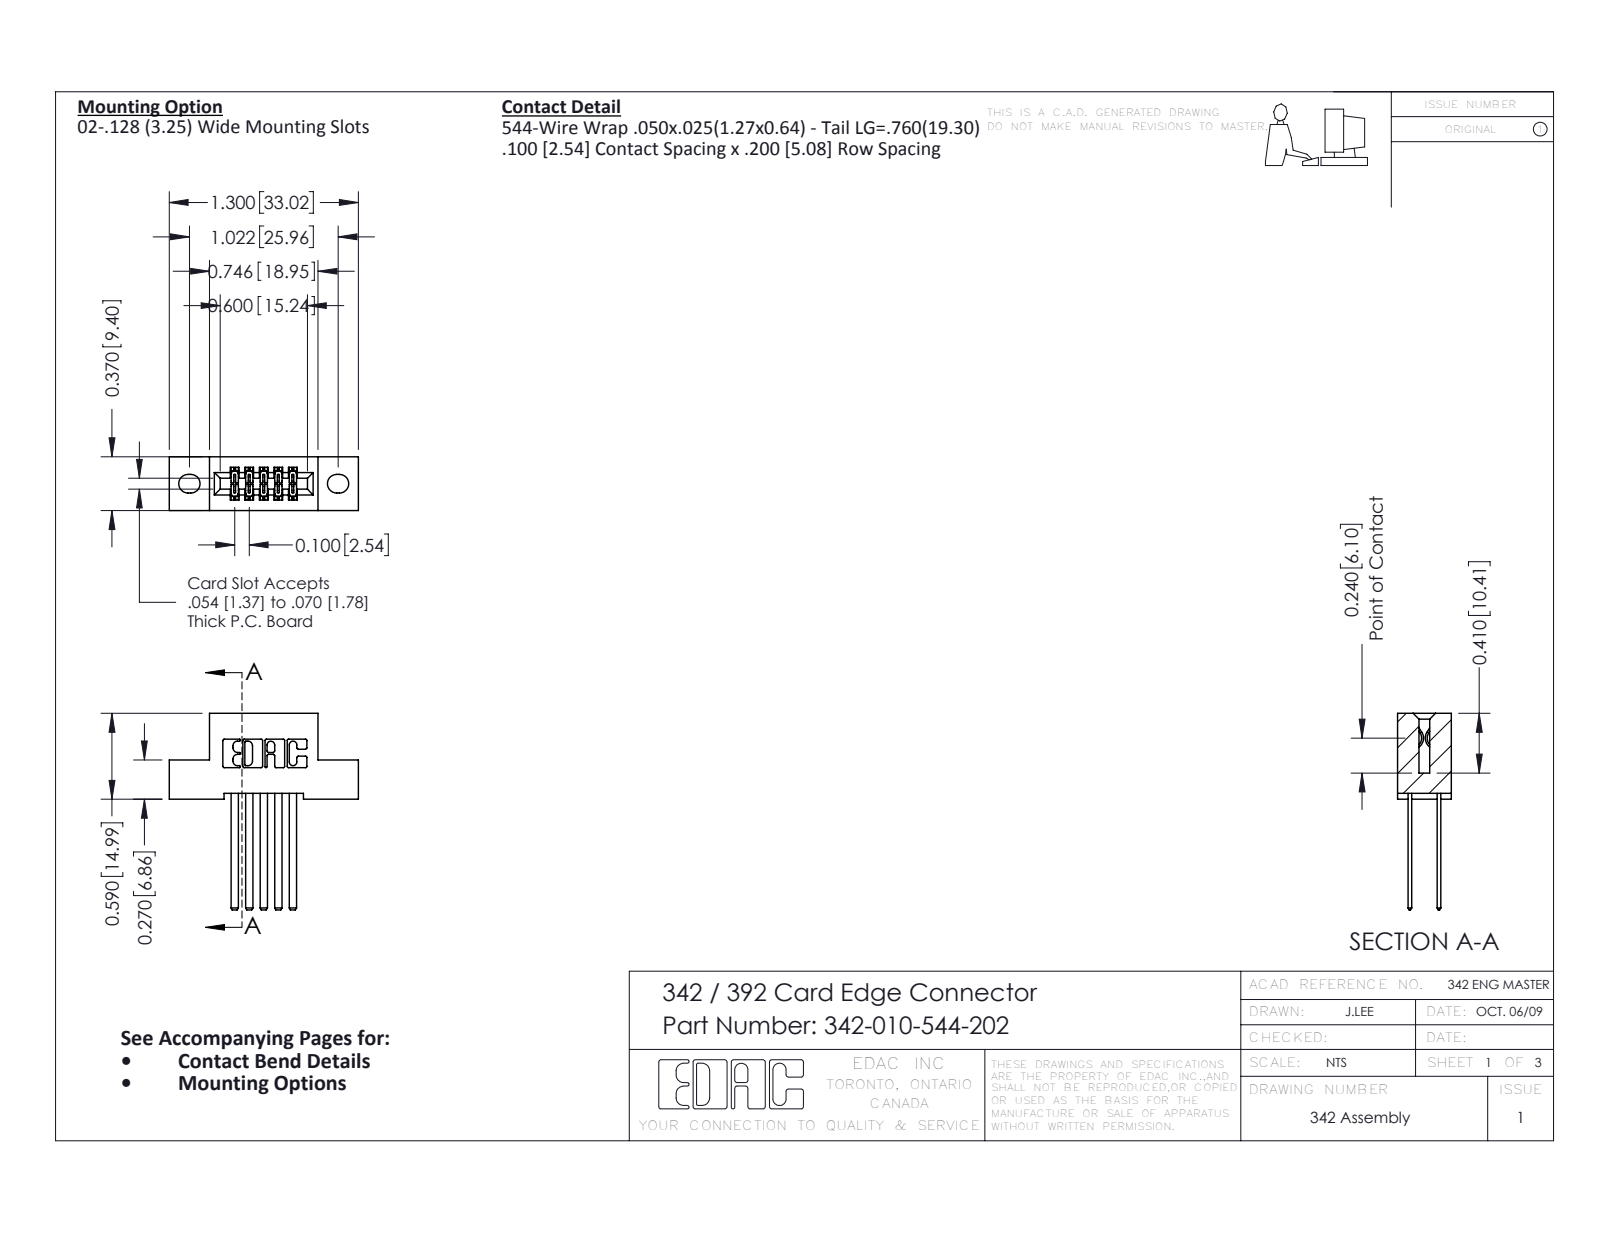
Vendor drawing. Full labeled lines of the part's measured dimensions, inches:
Part name (STEP PRODUCT): 342 Part_.128 Slot; 345-292-001_345-293-144; 342-010-544-202
STEP written by: SolidWorks 2016 (CONFIG_CONTROL_DESIGN)
Units: inches
Bodies: 11 solids, 574 faces (390 planar, 184 cylindrical, 0 other)
Overall size (bounding box): 1.35 × 1.3 × 0.37
Volume: 0.176 in³ · Surface area: 6.081 in²
Partial cylindrical surfaces — rounded edges, fillets, slot ends (radius × count): R0.01 ×22, R0.006 ×15, R0.007 ×6, R0.031 ×6, R0.064 ×4, R0.026 ×3, R0.014 ×2, R0.022 ×2
Main face-to-face distances: 0.2, 0.298, 0.072, 0.1, 0.098, 0.272, 0.025, 0.37, 0.04, 0.225
